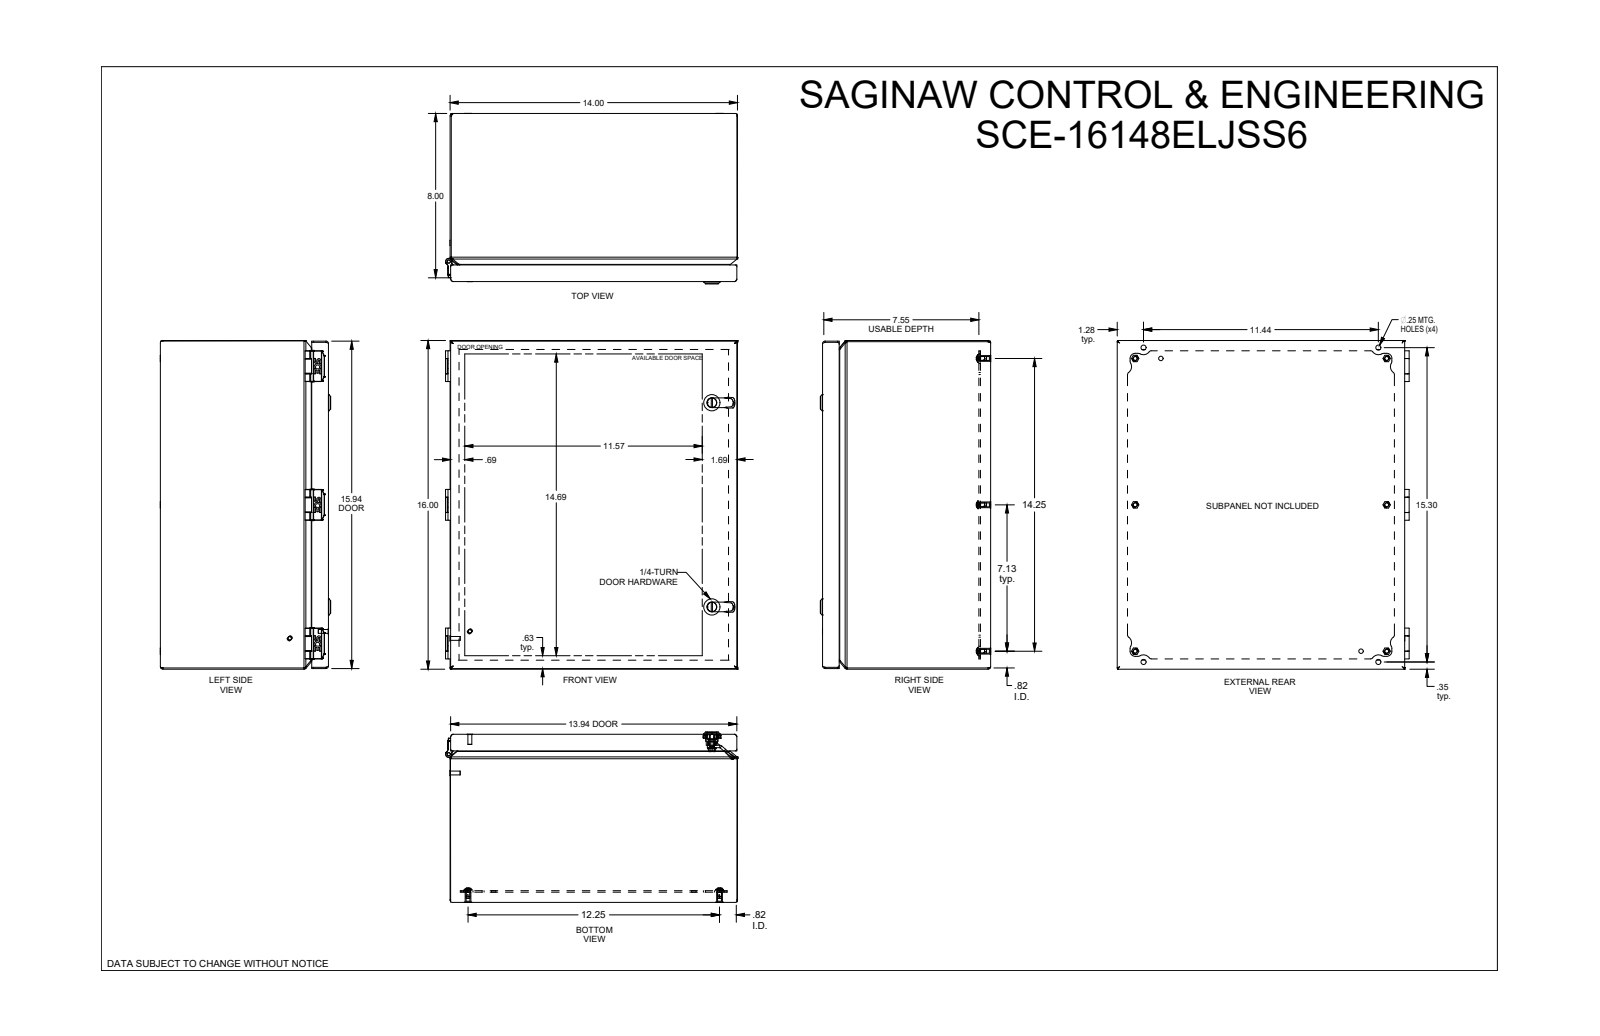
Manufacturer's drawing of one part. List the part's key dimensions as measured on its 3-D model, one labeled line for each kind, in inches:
Part name (STEP PRODUCT): SCE-16148ELJ
STEP written by: SolidWorks 2019 (AUTOMOTIVE_DESIGN)
Units: inches
Bodies: 51 solids, 2910 faces (796 planar, 819 cylindrical, 1295 other)
Overall size (bounding box): 16.06 × 14.22 × 8.296
Volume: 77.75 in³ · Surface area: 2 452 in²
Round holes (diameter × count): ⌀0.17 ×6, ⌀0.19 ×6, ⌀0.25 ×6, ⌀0.284 ×4, ⌀0.02 ×3, ⌀0.1 ×3, ⌀0.2 ×2, ⌀0.218 ×2, ⌀0.239 ×2, ⌀0.254 ×2, ⌀0.266 ×2, ⌀0.269 ×2
Round bosses / shafts (diameter × count): ⌀0.188 ×8, ⌀0.479 ×6, ⌀0.373 ×6, ⌀0.28 ×6, ⌀0.16 ×6, ⌀0.26 ×3, ⌀0.237 ×3, ⌀0.23 ×3
Partial cylindrical surfaces — rounded edges, fillets, slot ends (radius × count): R0.106 ×198, R0.005 ×114, R0.03 ×40, R0.025 ×36, R0.013 ×31, R0.01 ×18, R0.05 ×16, R0.25 ×13
Main face-to-face distances: 0.059, 0.06, 14.001, 8.185, 8.126, 8.125, 8.066, 16.001, 0.571, 0.512
Hole centre spacings: 6.75, 7.125, 14.171, 12.25, 13.5, 14.311, 0.06, 1.25
